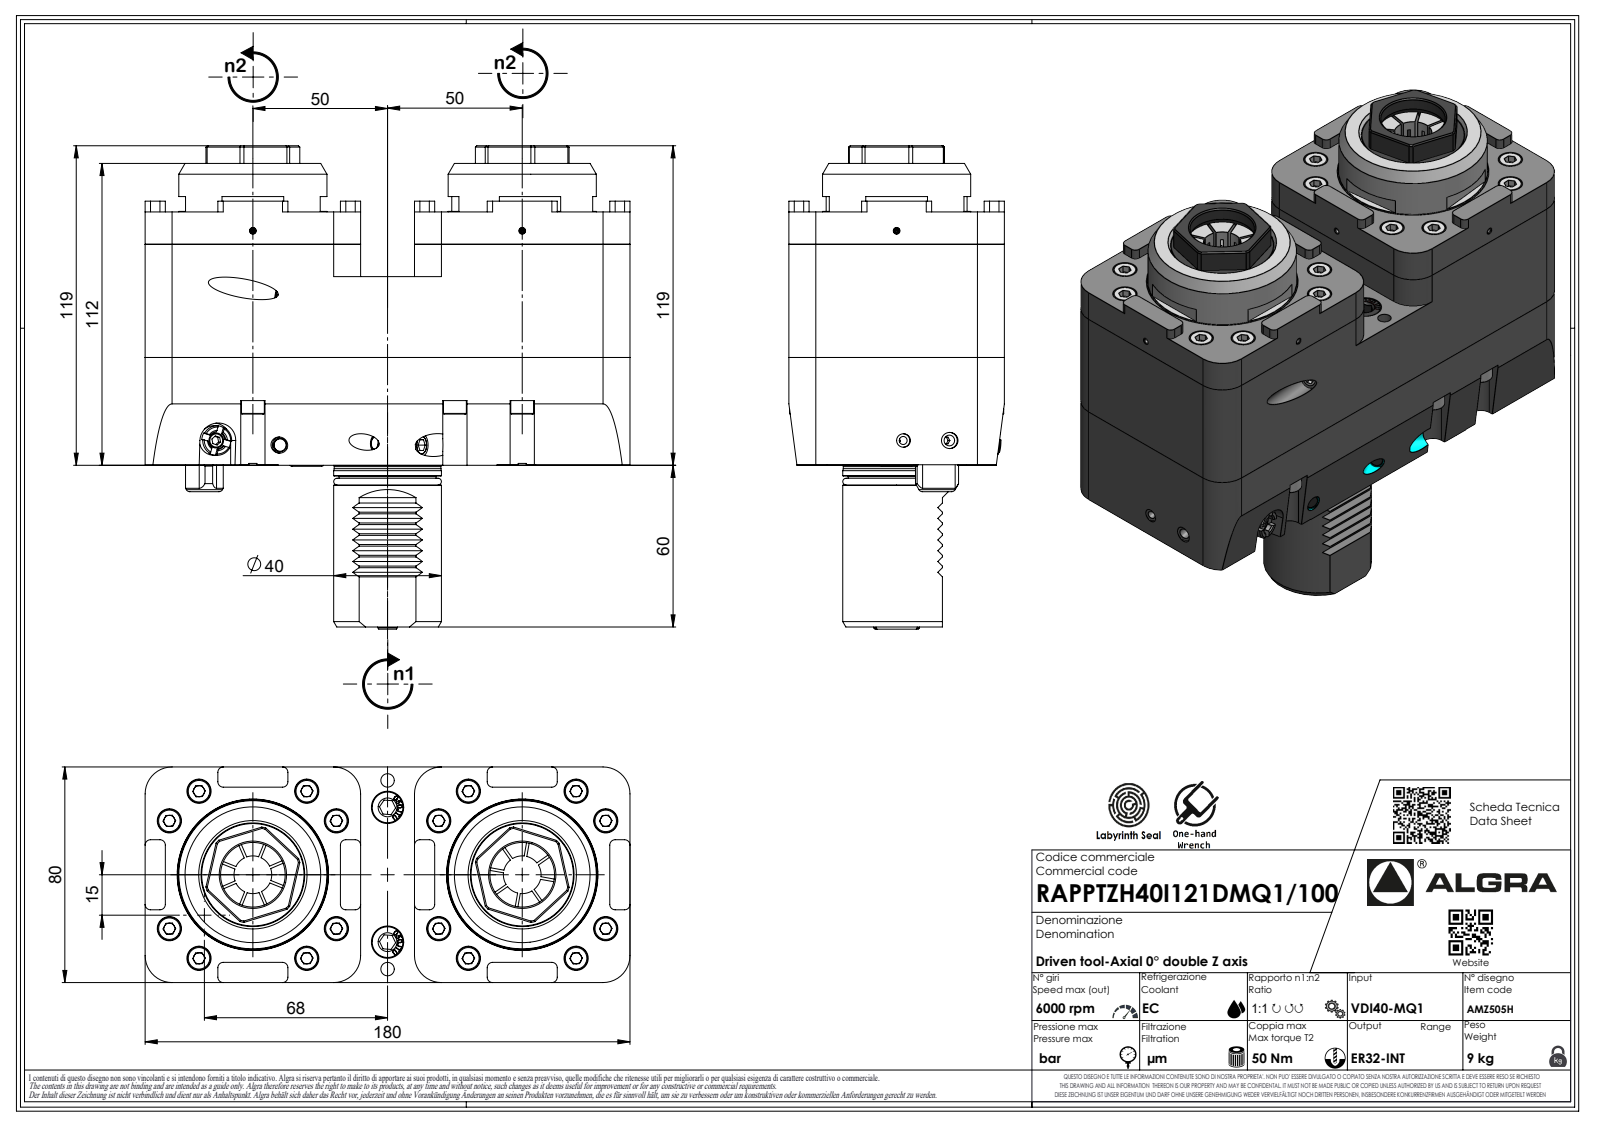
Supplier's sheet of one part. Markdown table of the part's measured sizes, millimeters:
| quantity | value |
| --- | --- |
| part name | RAPPTZH40I121DMQ1100 |
| STEP written by | SolidWorks 2023 (AUTOMOTIVE_DESIGN) |
| units | millimeters |
| bodies | 1 solid, 660 faces (436 planar, 123 cylindrical, 101 other) |
| overall size | 180 × 178.55 × 80 |
| volume | 1 456 000 mm³ |
| surface area | 97 470 mm² |
| round holes (diameter × count) | 2.1 × 1 |
| round bosses / shafts (diameter × count) | 55 × 2, 40 × 1, 39.6 × 1, 36 × 1, 6.37 × 1, 1.7 × 1 |
| partial cylindrical surfaces (radius × count) | 2 × 32, 10 × 8, 0.33 × 7, 0.52 × 7, 3.7 × 7, 4.5 × 6, 1.5 × 4, 5 × 4 |
| main face-to-face distances | 80, 94, 180, 93.8, 100, 112, 111.8, 18, 24, 70 |
